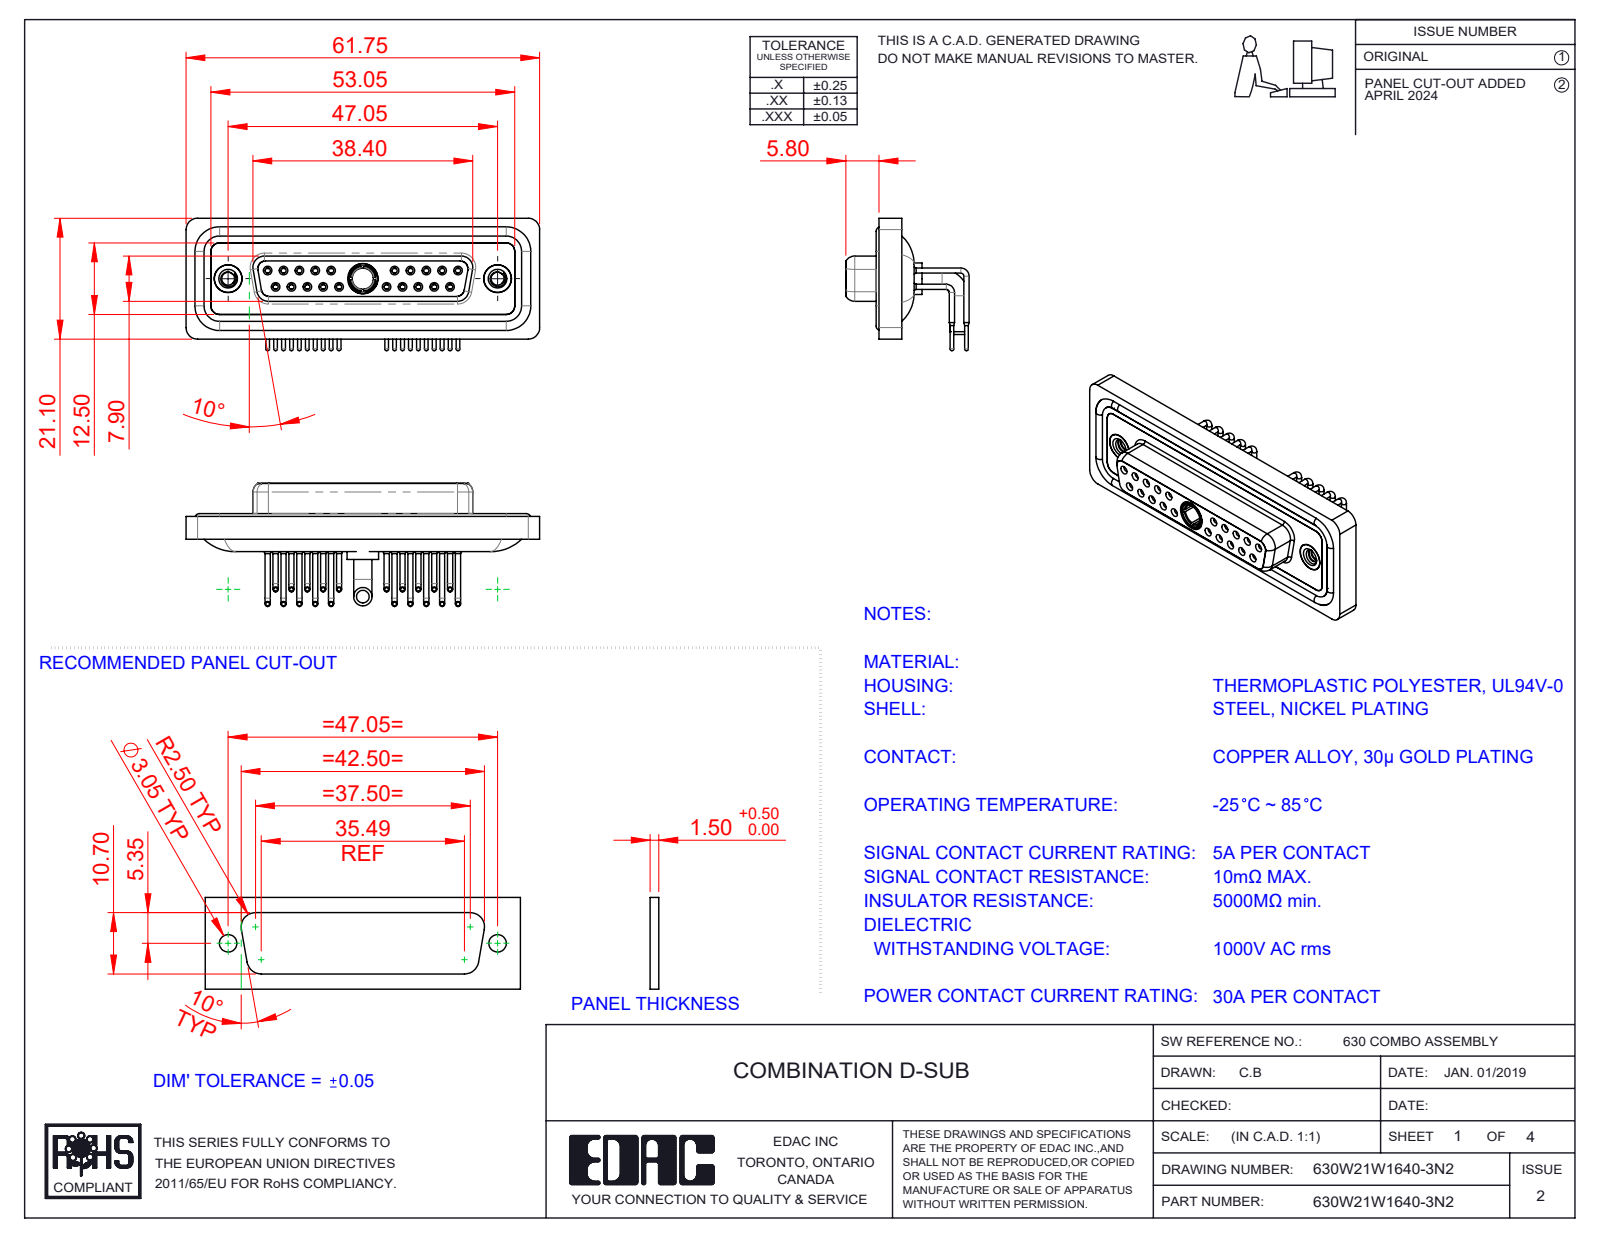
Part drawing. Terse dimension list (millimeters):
name: 630Combo Housing_21W1; Power Socket_30A RA; 630W21W1640-3N2; 630Combo Shell Front_25 Contacts (+5 more)
written by: SolidWorks 2023 (CONFIG_CONTROL_DESIGN)
unit: mm
bodies: 29 solids, 1524 faces (434 planar, 673 cylindrical, 417 other)
size: 61.75 × 23.12 × 21.53
volume: 8 533 mm³; area: 14 798 mm²
holes: 20× ⌀0.9, 20× ⌀1.1, 20× ⌀1.5, 20× ⌀2, 10× ⌀1.6, 10× ⌀1.7, 3× ⌀4.85, 2× ⌀2.26, 2× ⌀4, 2× ⌀4.05, 2× ⌀5, 1× ⌀3.7
bosses: 20× ⌀0.9, 20× ⌀0.65, 14× ⌀1.6, 2× ⌀4.95, 2× ⌀4.8, 2× ⌀3.2, 1× ⌀5.5, 1× ⌀5.2
rounds: 18× R1.5, 18× R2, 8× R1.35, 8× R1.6, 4× R0.25, 4× R0.5, 4× R0.6, 4× R0.65
face distances: 0.4, 1.8, 4.1, 1.6, 1.1, 2.5, 3.1, 1.5, 9.8, 0.45
hole spacings: 3.16, 2.77, 5.54, 8.31, 5.04, 19.39, 20.97, 22.16
